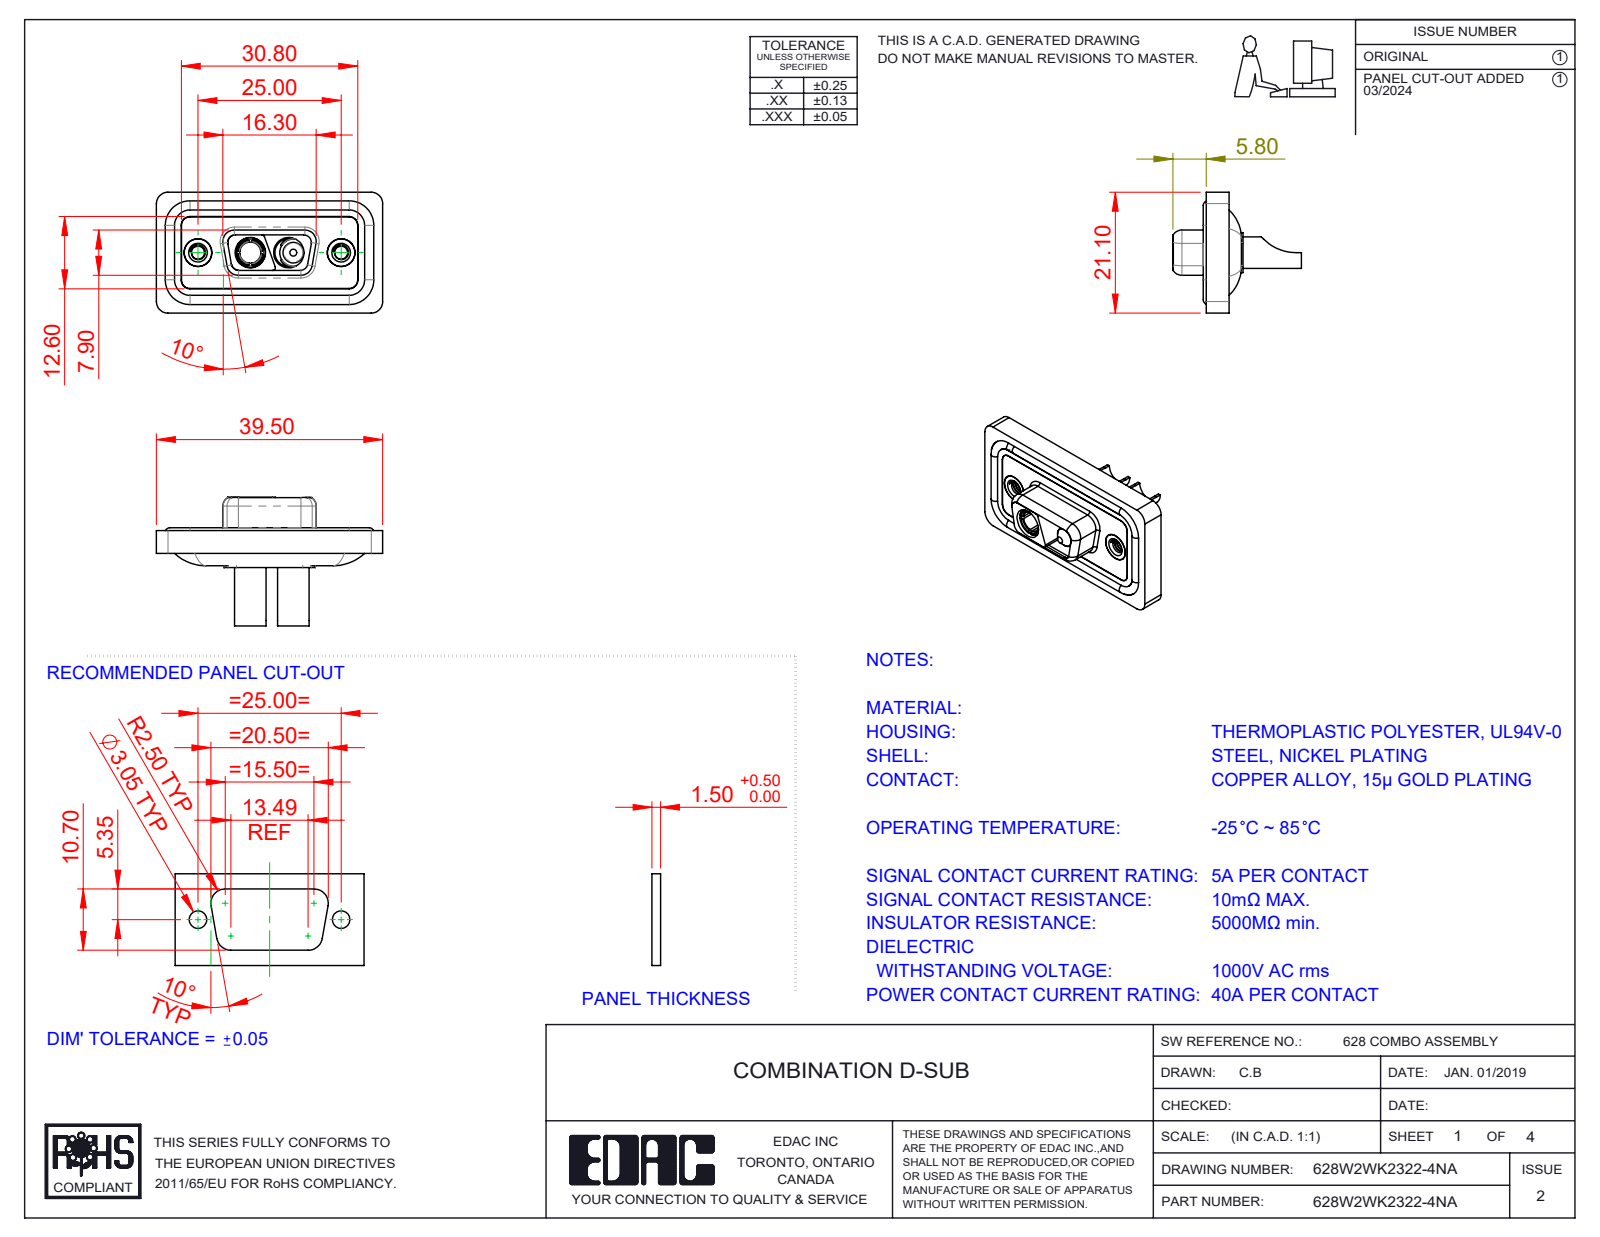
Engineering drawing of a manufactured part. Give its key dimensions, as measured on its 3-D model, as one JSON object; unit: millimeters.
{"part_name": "628Combo Threaded Rivet_A; 628Combo Shell Rear_09 Contacts; Power Socket_40A SC; 628Combo Housing_2WK2 (+4 more)", "step_written_by": "SolidWorks 2023 (CONFIG_CONTROL_DESIGN)", "units": "millimeters", "bodies": {"solids": 11, "faces": 504, "planar": 148, "cylindrical": 235, "other": 121}, "overall_size": [39.5, 22.45, 21.1], "volume_mm3": 4684, "surface_area_mm2": 7621, "round_holes": [[4.85, 4], [2.26, 2], [4, 2], [4.05, 2], [4.6, 2], [5, 2], [5.3, 2], [3.7, 1]], "round_bosses_or_shafts": [[1.6, 4], [5.5, 2], [5.2, 2], [4.95, 2], [4.8, 2], [4.75, 2], [3.75, 2], [4.96, 1]], "partial_cylinders_radius": [[1.5, 22], [2, 18], [1.35, 8], [1.6, 8], [0.5, 6], [0.25, 4], [0.6, 4], [0.65, 4]], "face_to_face_distances": [0.4, 1.1, 2.9, 1.6, 0.5, 1.8, 5.65, 5.35, 3.1, 0.7], "hole_center_spacings": [9.14, 15.86, 6.72, 25]}
